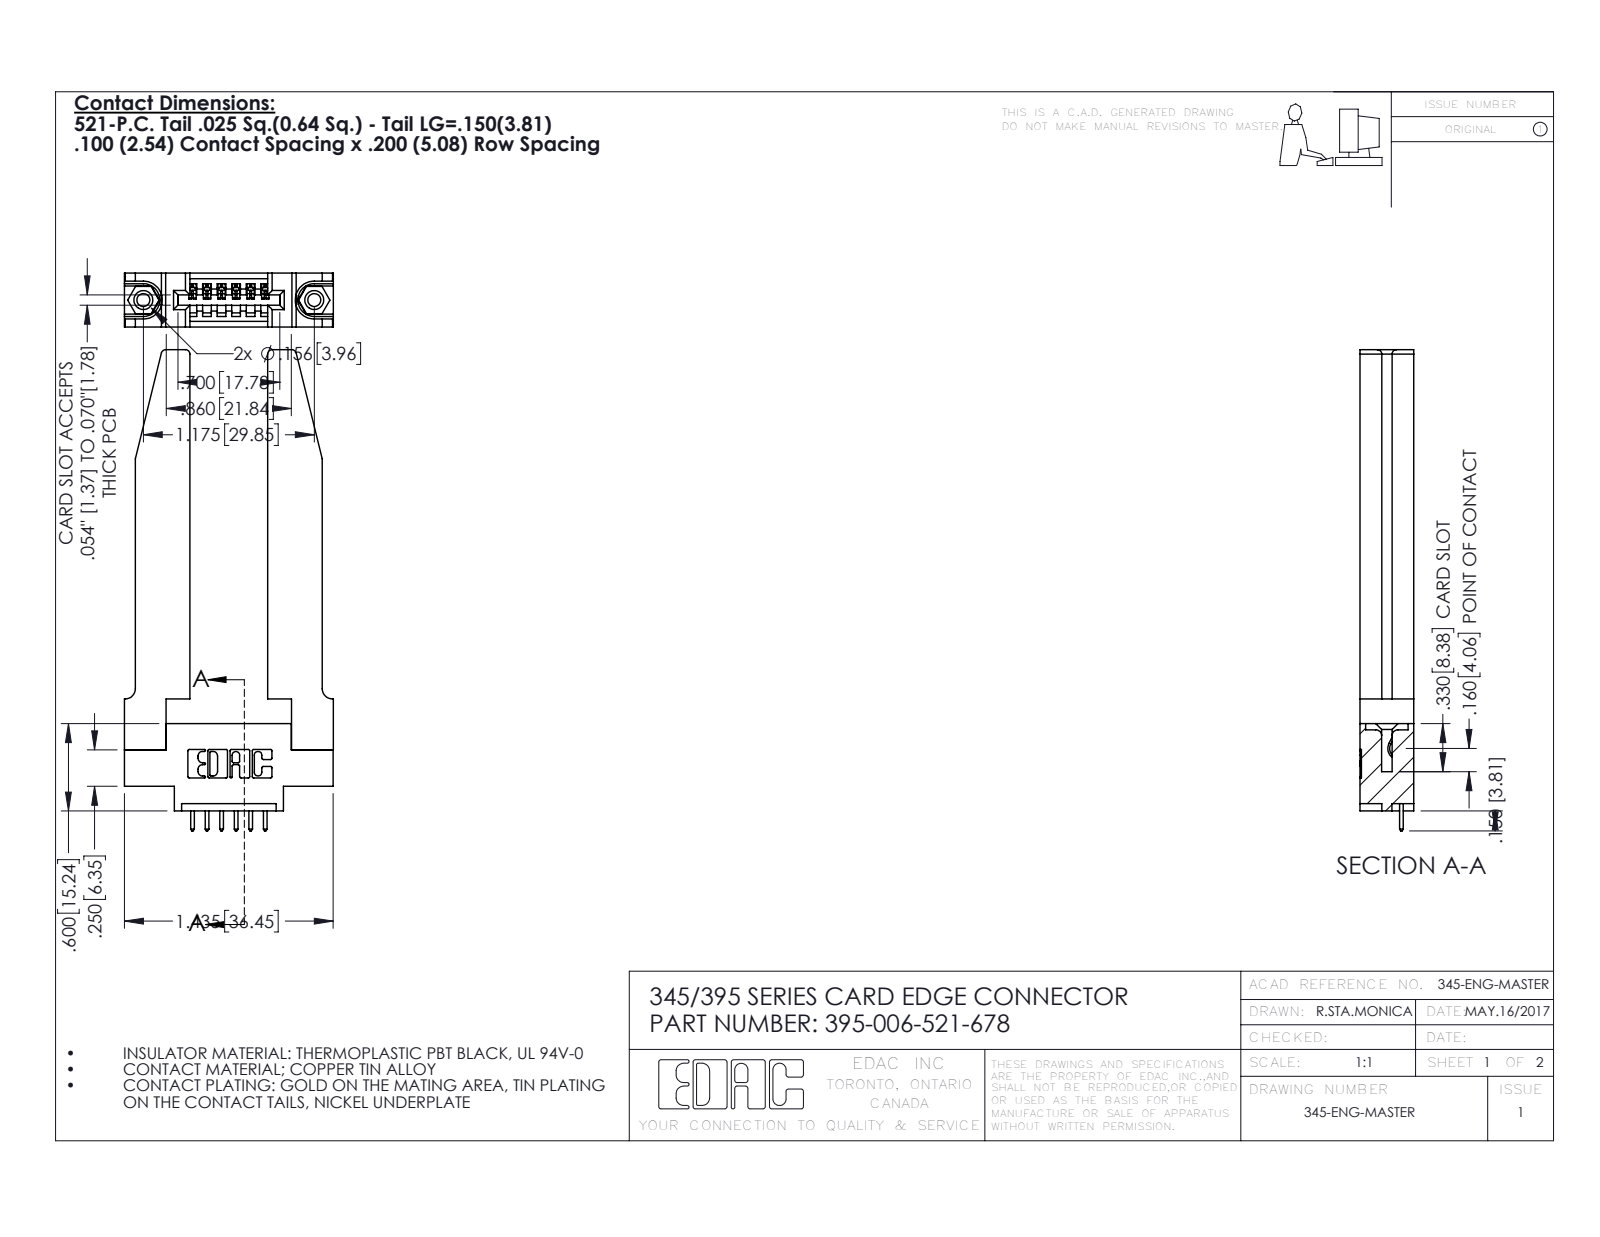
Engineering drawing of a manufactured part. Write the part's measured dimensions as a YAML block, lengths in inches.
part_name: "345-292-001_345-293-121; 345-250-001_345-250-001-102; 345-220-078_345-220-078; 395-006-521-678 (+1 more)"
step_written_by: "SolidWorks 2016 (CONFIG_CONTROL_DESIGN)"
units: inches
bodies: {solids: 11, faces: 712, planar: 466, cylindrical: 194, other: 52}
overall_size: [3.307, 1.436, 0.37]
volume: 0.66
surface_area: 16.2
round_holes:
  - {diameter: 0.089, count: 2}
  - {diameter: 0.125, count: 2}
  - {diameter: 0.156, count: 2}
  - {diameter: 0.064, count: 1}
round_bosses_or_shafts:
  - {diameter: 0.155, count: 2}
partial_cylinders:
  - {radius: 0.01, count: 22}
  - {radius: 0.006, count: 12}
  - {radius: 0.01, count: 12}
  - {radius: 0.03, count: 8}
  - {radius: 0.007, count: 6}
  - {radius: 0.031, count: 6}
  - {radius: 0.026, count: 3}
  - {radius: 0.031, count: 2}
face_to_face_distances: [0.37, 0.15, 0.22, 0.535, 0.072, 0.148, 0.298, 0.077, 0.095, 0.071]
hole_center_spacings: [0.27, 0.946, 1.175]
